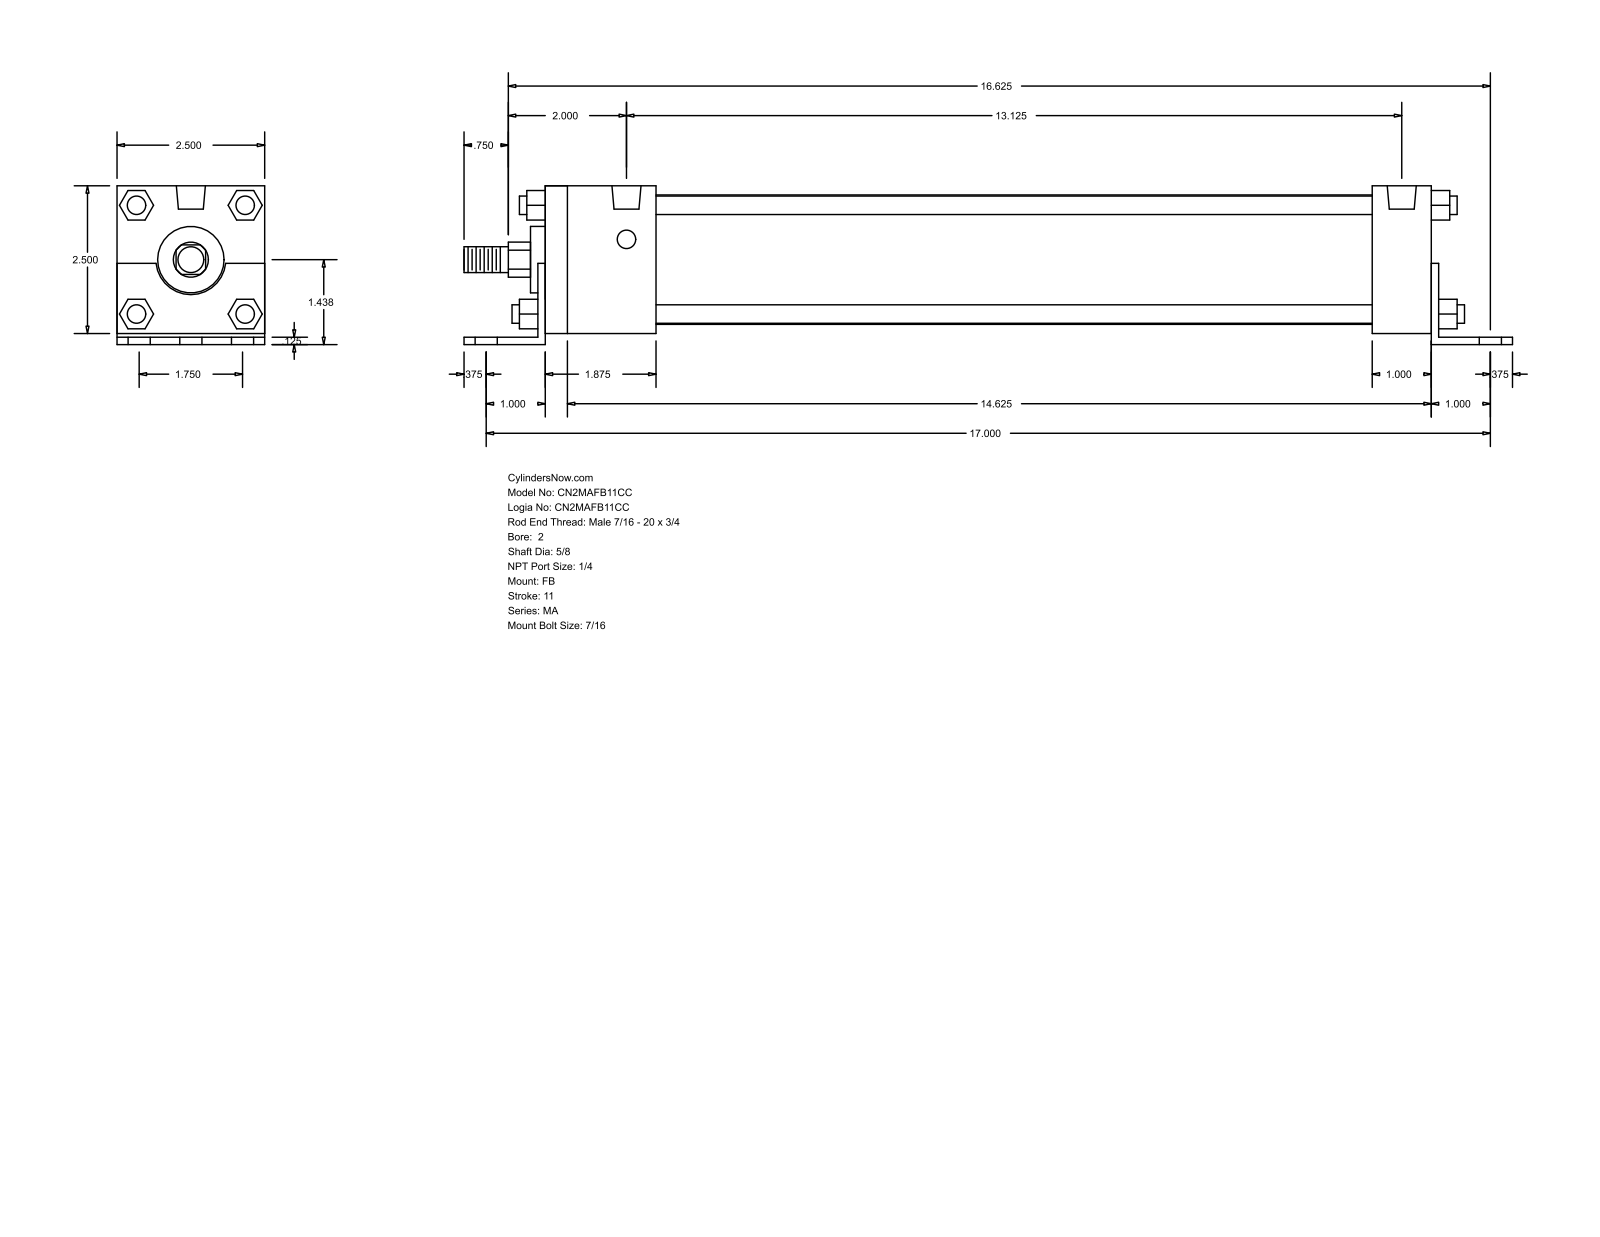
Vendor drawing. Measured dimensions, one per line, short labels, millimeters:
name: MA_FB__0200_0.625
written by: GSSL Pune (CONFIG_CONTROL_DESIGN)
unit: mm
bodies: 0 solids, 140 faces (105 planar, 35 cylindrical, 0 other)
size: 450.85 × 68.26 × 63.5
holes: 6× ⌀11.11, 4× ⌀7.94, 2× ⌀12.49
bosses: 4× ⌀7.94, 1× ⌀55.63, 1× ⌀28.57, 1× ⌀15.88, 1× ⌀11.11
rounds: 1× R7.54, 1× R15.05
face distances: 63.5, 3.17, 4.76, 68.26, 1.59, 65.09, 387.35, 3.18, 381, 384.17
hole spacings: 22.23, 432.37, 431.8, 44.1, 44.46, 64.3, 333.38, 372.13
